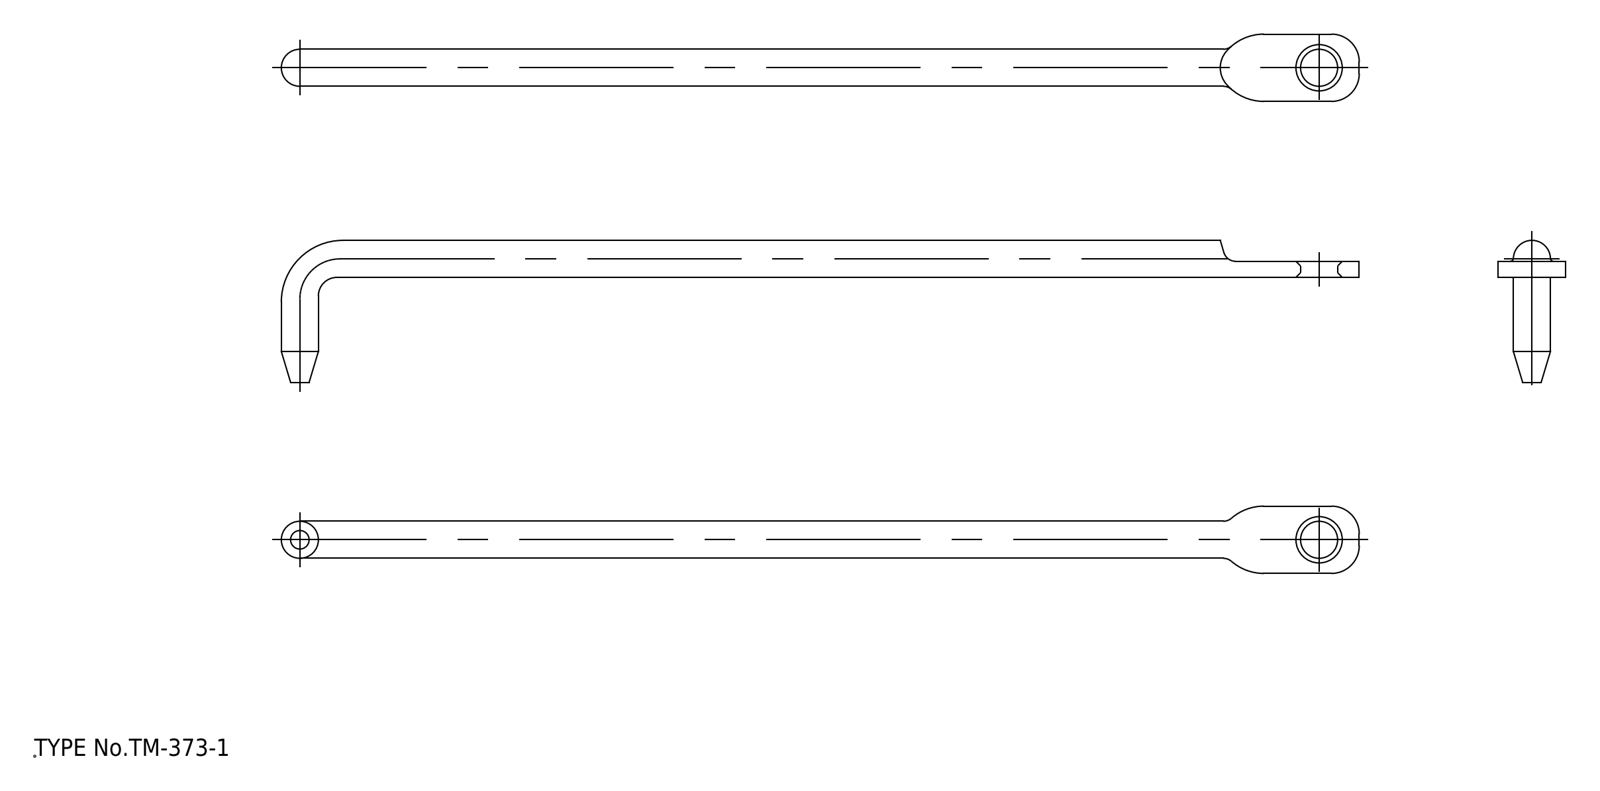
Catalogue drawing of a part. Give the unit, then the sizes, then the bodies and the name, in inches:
Units: inches
Overall size (bounding box): 6.87 × 0.906 × 0.429
Round holes (diameter × count): ⌀0.236 ×1
Round bosses / shafts (diameter × count): ⌀0.236 ×2
Partial cylindrical surfaces — rounded edges, fillets, slot ends (radius × count): R0.177 ×2, R0.315 ×2, R0.079 ×1
Main face-to-face distances: 0.102, 0.429, 0.772, 0.669
Volume: 0.312 in³ · Surface area: 5.701 in²
Bodies: 1 solid, 28 faces (7 planar, 11 cylindrical, 10 other)
STEP written by: spGate 19.8.4 (****-****-****-****) (AUTOMOTIVE_DESIGN)
